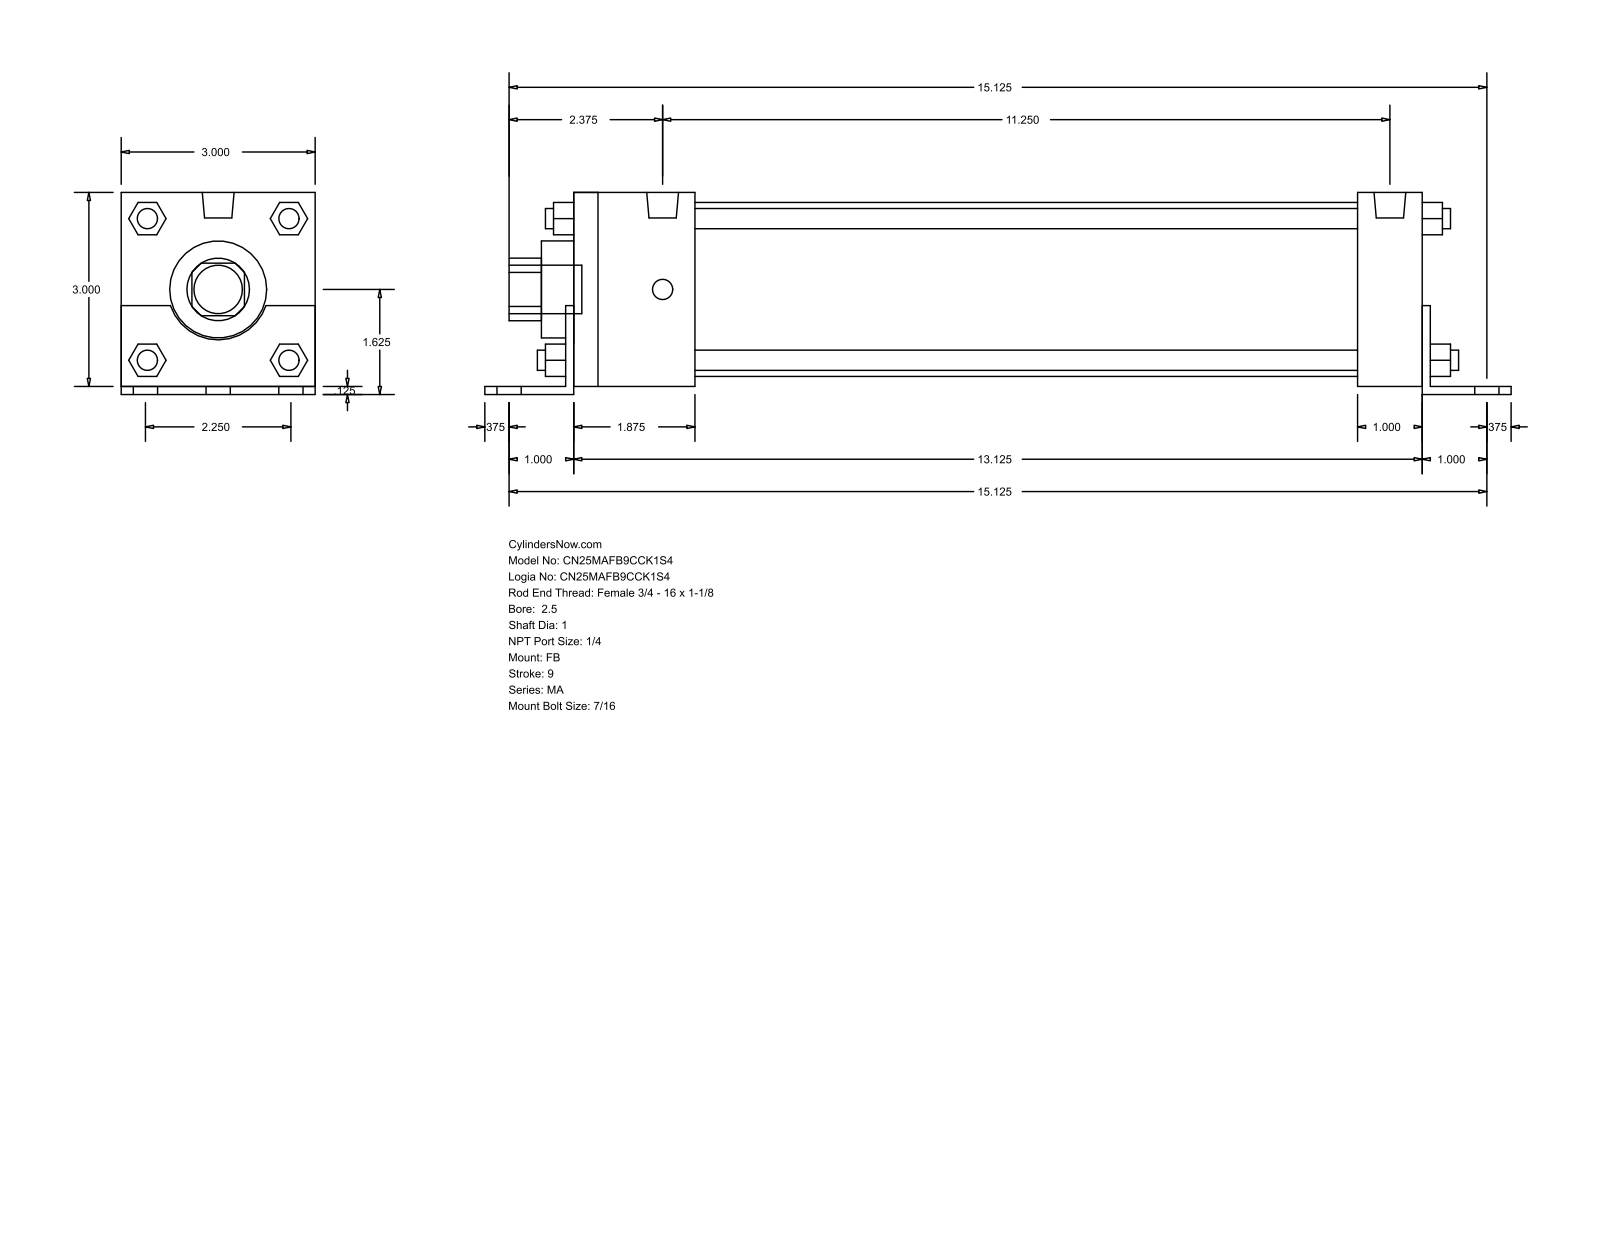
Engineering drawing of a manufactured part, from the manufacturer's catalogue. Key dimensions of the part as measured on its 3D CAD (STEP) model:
Part name (STEP PRODUCT): MA_FB__0250_1
STEP written by: GSSL Pune (CONFIG_CONTROL_DESIGN)
Units: millimetres
Bodies: 0 solids, 140 faces (105 planar, 35 cylindrical, 0 other)
Overall size (bounding box): 403.23 × 79.38 × 76.2
Round holes (diameter × count): ⌀25.4 ×1, ⌀38.1 ×1, ⌀68.33 ×1
Round bosses / shafts (diameter × count): ⌀7.94 ×8, ⌀11.11 ×6, ⌀12.49 ×2, ⌀19.05 ×1
Partial cylindrical surfaces — rounded edges, fillets, slot ends (radius × count): R12.29 ×1, R19.81 ×1
Main face-to-face distances: 76.2, 3.17, 79.37, 333.37, 3.18, 12.7, 336.55, 28.57, 47.63, 285.74
